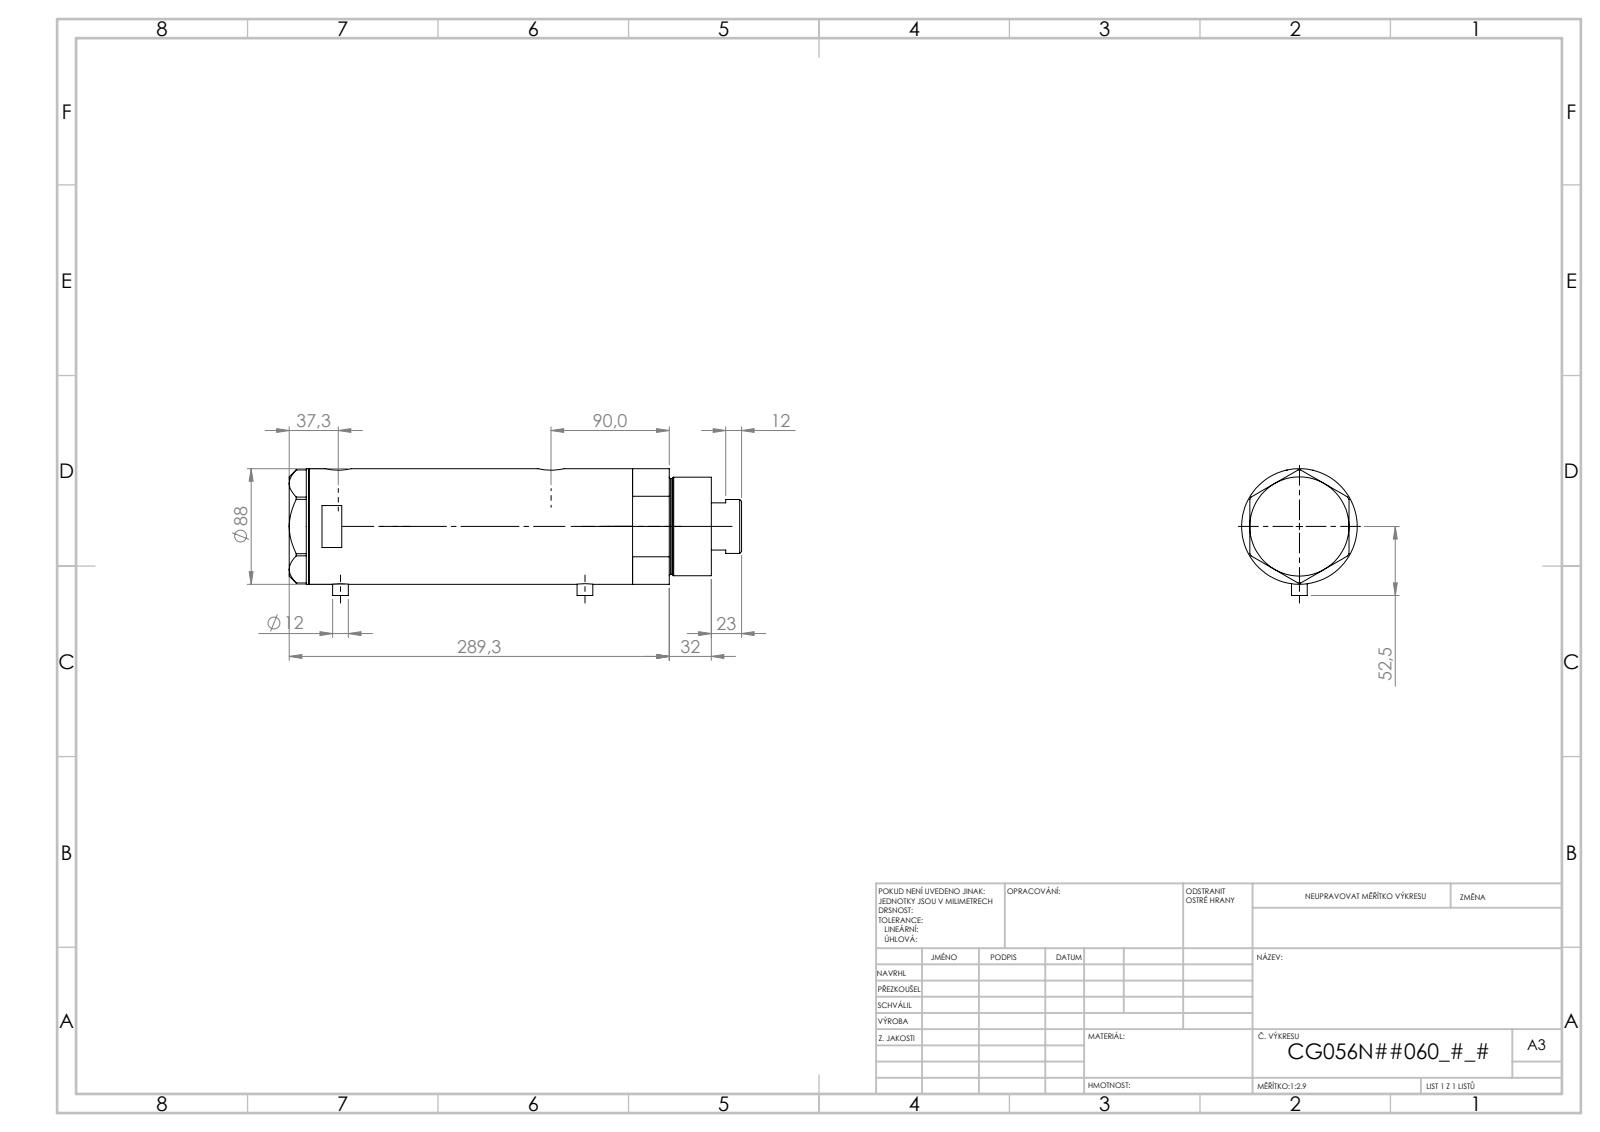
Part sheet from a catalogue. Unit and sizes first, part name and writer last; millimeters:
Units: millimetres
Overall size (bounding box): 284.47 × 89.1 × 88
Round holes (diameter × count): ⌀5 ×2, ⌀12.5 ×2, ⌀13.16 ×2, ⌀20 ×2, ⌀14.5 ×1, ⌀42 ×1, ⌀43.5 ×1, ⌀56 ×1, ⌀60 ×1, ⌀80 ×1
Round bosses / shafts (diameter × count): ⌀12 ×2, ⌀88 ×1, ⌀75 ×1, ⌀73 ×1, ⌀41 ×1
Main face-to-face distances: 134.4, 26, 108.4, 15, 41, 149.4, 246.47, 261.47, 220.47, 112.07
Hole centre spacings: 1.7, 25.8, 110.3, 112, 136.1, 137.8
Volume: 1 462 000 mm³ · Surface area: 215 320 mm²
Bodies: 4 solids, 126 faces (53 planar, 53 cylindrical, 20 other)
Part name (STEP PRODUCT): V270CG_VC; V270CG_MIDDLE; V270CG_BACK; V270CG_FRONT
STEP written by: SolidWorks 2019 (CONFIG_CONTROL_DESIGN)
